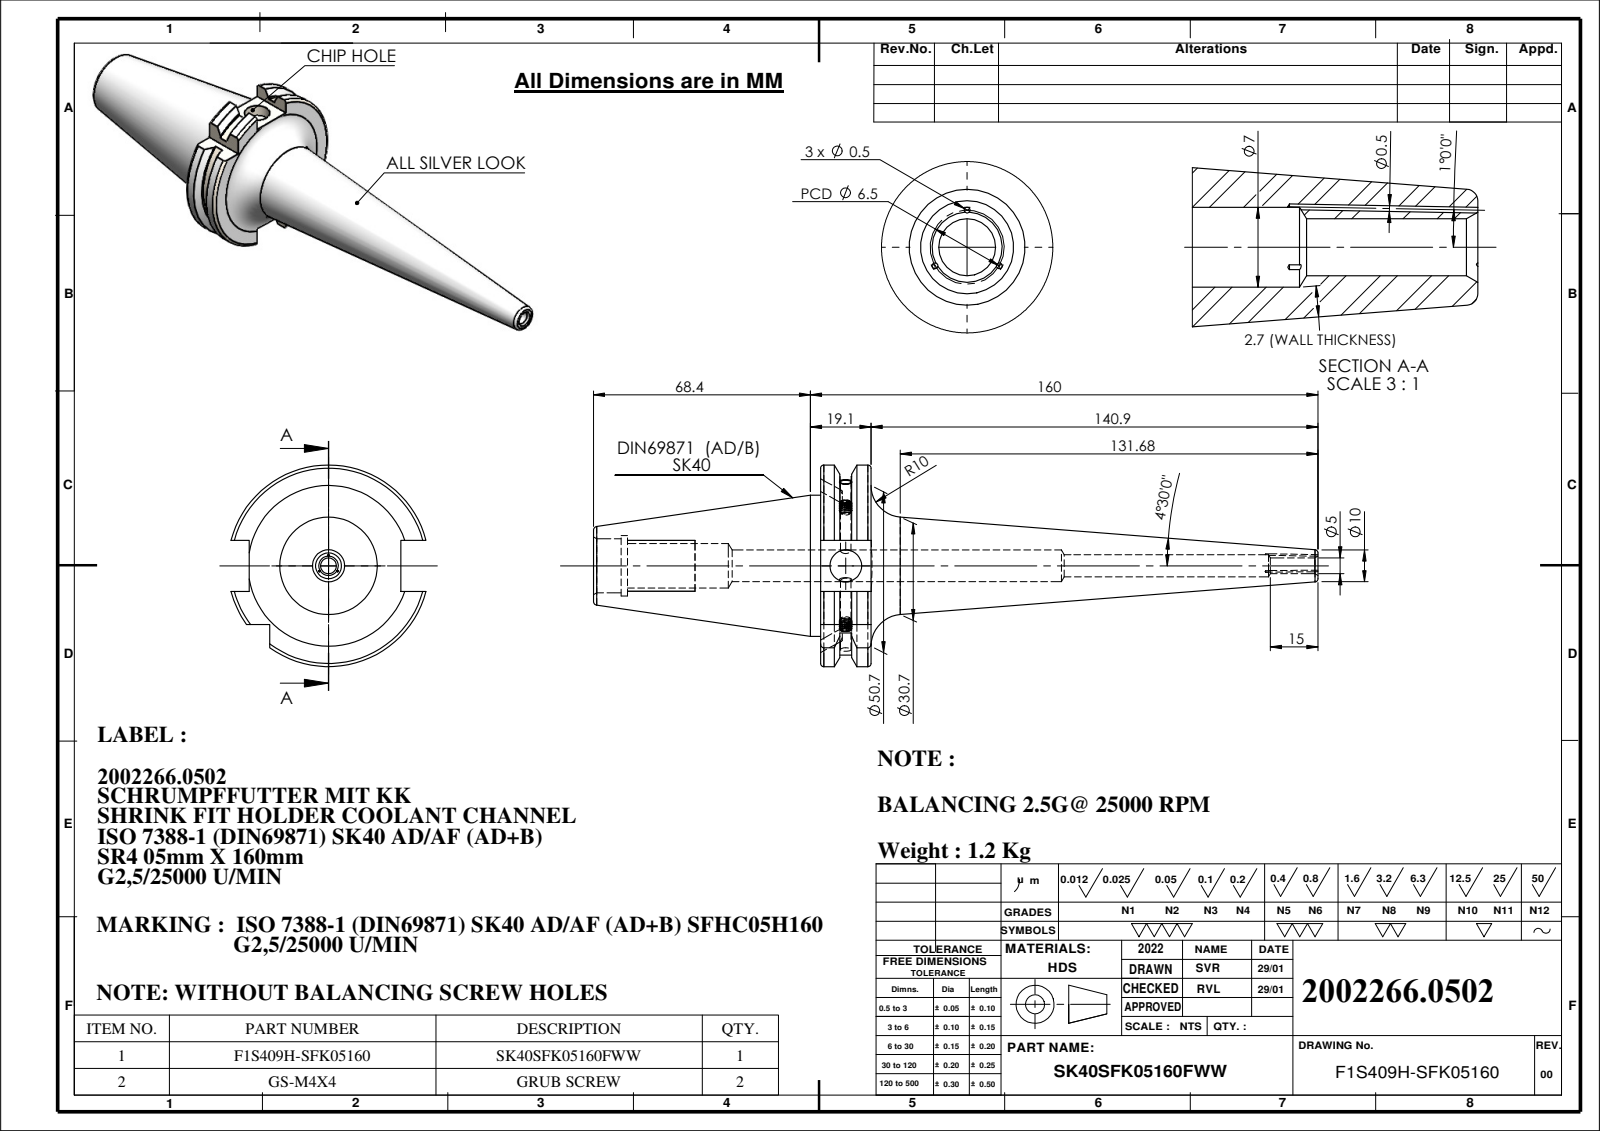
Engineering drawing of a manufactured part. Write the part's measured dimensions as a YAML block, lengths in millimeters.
part_name: "91406-SR405160; GS-M4X4_DIN 913 - M4 x 4-N; SK40SFK05160FWW"
step_written_by: "SolidWorks 2018 (CONFIG_CONTROL_DESIGN)"
units: millimeters
bodies: {solids: 3, faces: 207, planar: 47, cylindrical: 58, other: 102}
overall_size: [228.4, 63.55, 61.48]
volume: 149878
surface_area: 33091
round_holes:
  - {diameter: 0.5, count: 3}
  - {diameter: 10, count: 2}
  - {diameter: 3.3, count: 1}
  - {diameter: 4.99, count: 1}
  - {diameter: 7, count: 1}
  - {diameter: 14, count: 1}
  - {diameter: 17, count: 1}
  - {diameter: 19, count: 1}
round_bosses_or_shafts:
  - {diameter: 4, count: 2}
  - {diameter: 44.45, count: 1}
partial_cylinders:
  - {radius: 28.12, count: 1}
  - {radius: 31.77, count: 1}
face_to_face_distances: [15.9, 16.1, 47.8, 71.6, 87.5, 10.7, 60.9, 76.8, 77.63, 66.93]
